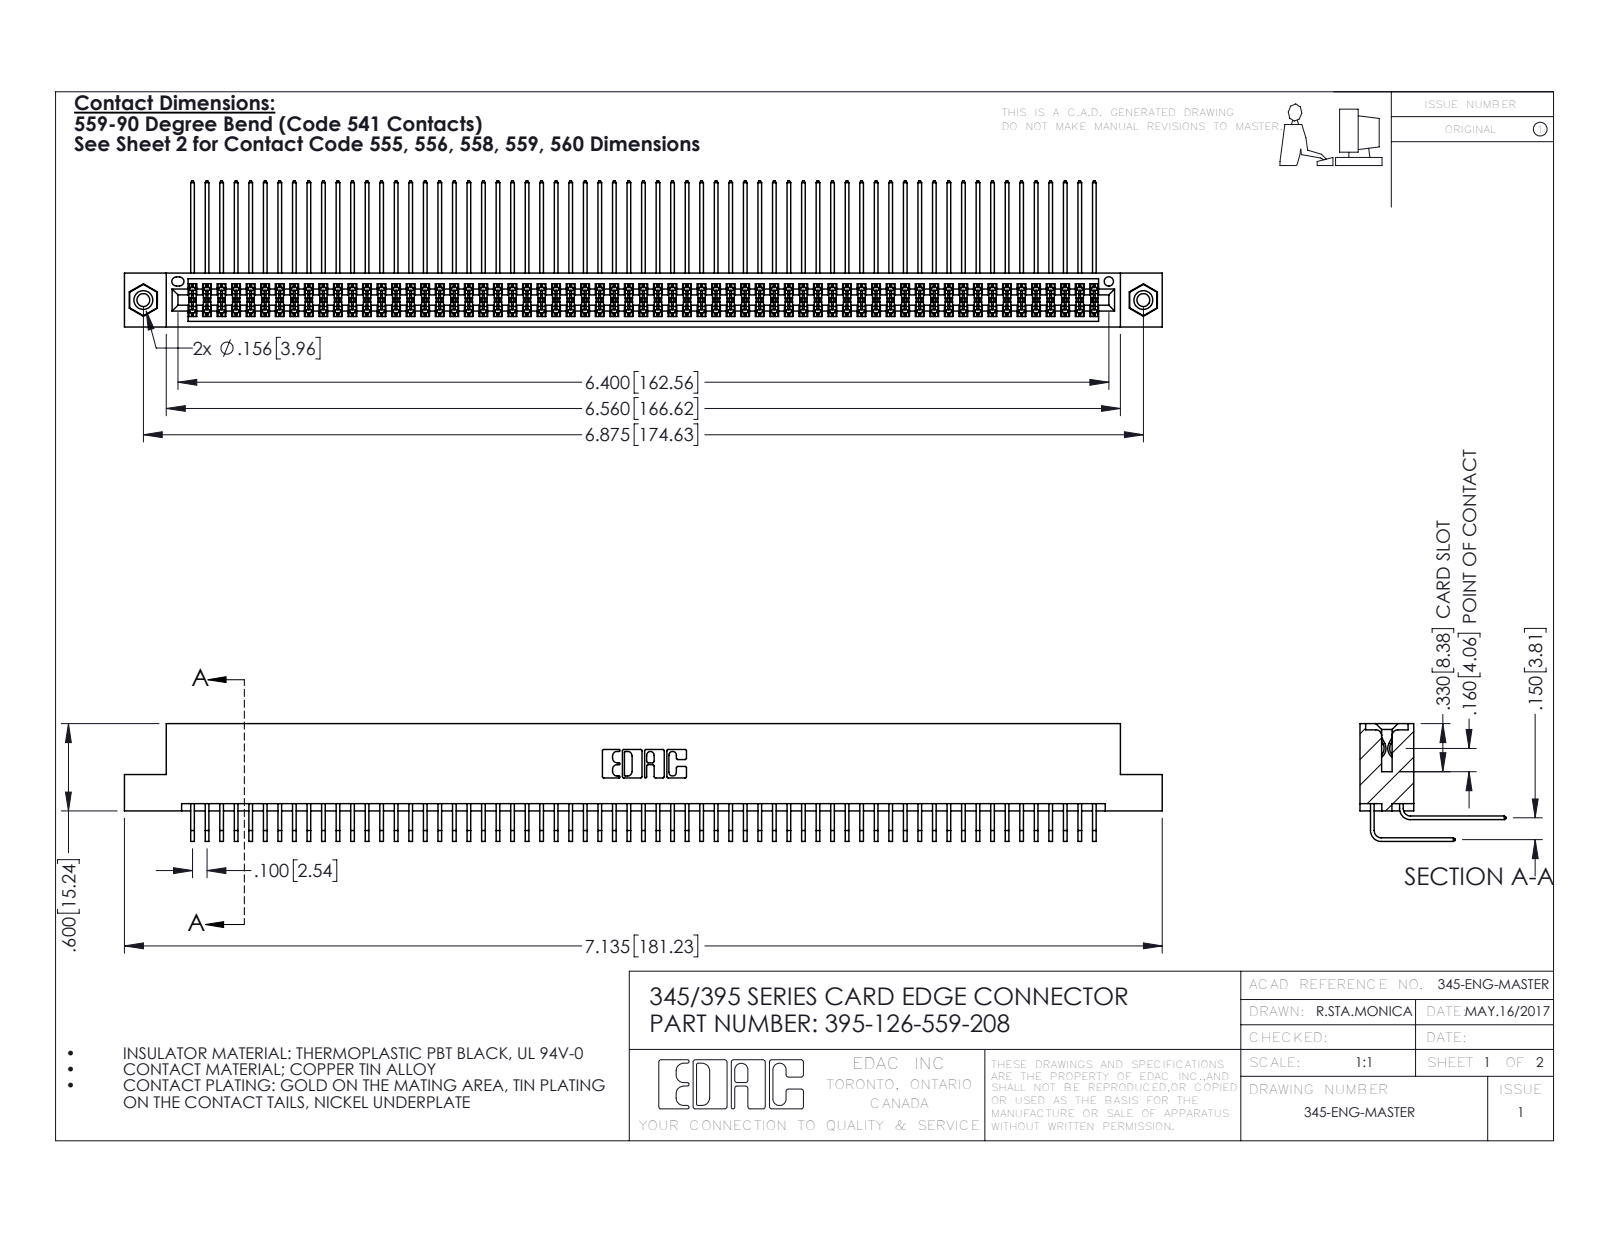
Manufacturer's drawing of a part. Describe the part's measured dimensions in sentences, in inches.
The part is named "395-126-559-208; 345-250-001_345-250-003-102; 345-292-001_559 Tail - 2; 345 Part_Flush Mounting Lugs - 0.156 Dia-TI (+1 more)". Its 3-D file was written by "SolidWorks 2016 (CONFIG_CONTROL_DESIGN)". It is 129 solids with 6738 faces: 4522 planar, 2200 cylindrical and 16 other. Overall it measures 7.135 by 1.005 by 0.809 inches. Its volume is 1.13 cubic inches and its surface area 48.38 square inches. Round holes: 2 of diameter 0.089, 2 of diameter 0.125, 2 of diameter 0.156, 1 of diameter 0.064. Round bosses or shafts: 2 of diameter 0.155. Partial cylindrical surfaces (rounded edges, fillets, slot ends): 189 of radius 0.006, 22 of radius 0.01, 6 of radius 0.007, 6 of radius 0.031, 3 of radius 0.026, 2 of radius 0.014, 2 of radius 0.019, 2 of radius 0.022. The main face-to-face distances are 0.072, 0.298, 0.2, 0.37, 0.098, 0.272, 0.025, 0.225, 0.175, 0.15. The hole center spacings are 0.27, 6.639, 6.875.
